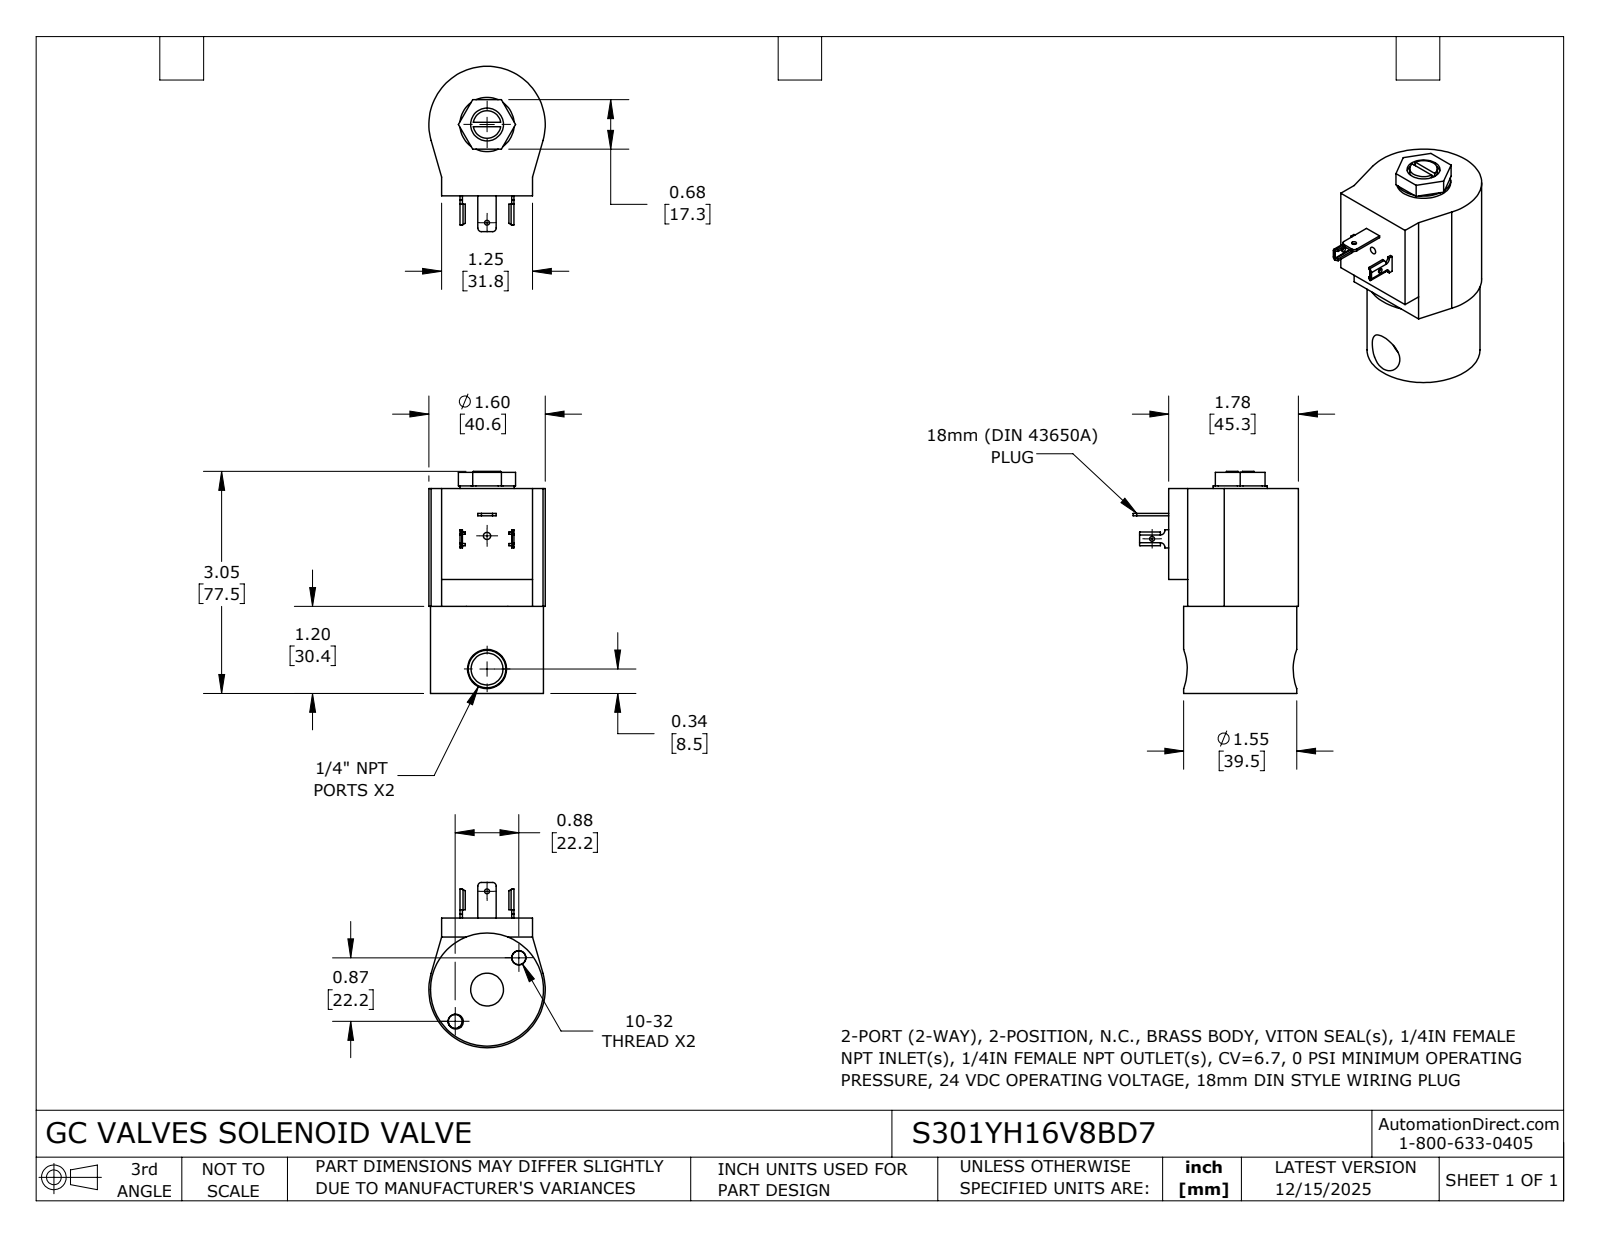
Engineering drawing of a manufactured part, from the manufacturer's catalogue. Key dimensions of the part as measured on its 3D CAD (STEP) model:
Part name (STEP PRODUCT): S301YH16V8BD7
STEP written by: SolidWorks 2024 (CONFIG_CONTROL_DESIGN)
Units: inches
Bodies: 2 solids, 171 faces (78 planar, 71 cylindrical, 22 other)
Overall size (bounding box): 3.061 × 2.273 × 1.6
Volume: 5.834 in³ · Surface area: 27.56 in²
Round holes (diameter × count): ⌀0.19 ×2, ⌀0.066 ×1, ⌀0.067 ×1, ⌀0.1 ×1, ⌀0.438 ×1, ⌀0.451 ×1
Round bosses / shafts (diameter × count): ⌀1.553 ×1, ⌀0.746 ×1, ⌀0.38 ×1
Partial cylindrical surfaces — rounded edges, fillets, slot ends (radius × count): R0.006 ×4, R0.041 ×4, R0.05 ×2, R0.06 ×2, R0.8 ×1
Main face-to-face distances: 1.62, 1.195, 2.815, 0.26, 1.565, 0.37, 1.25, 1.25, 3.038, 1.843
Hole centre spacings: 0.618, 0.619, 1.012, 1.237, 1.35, 1.83, 1.84
